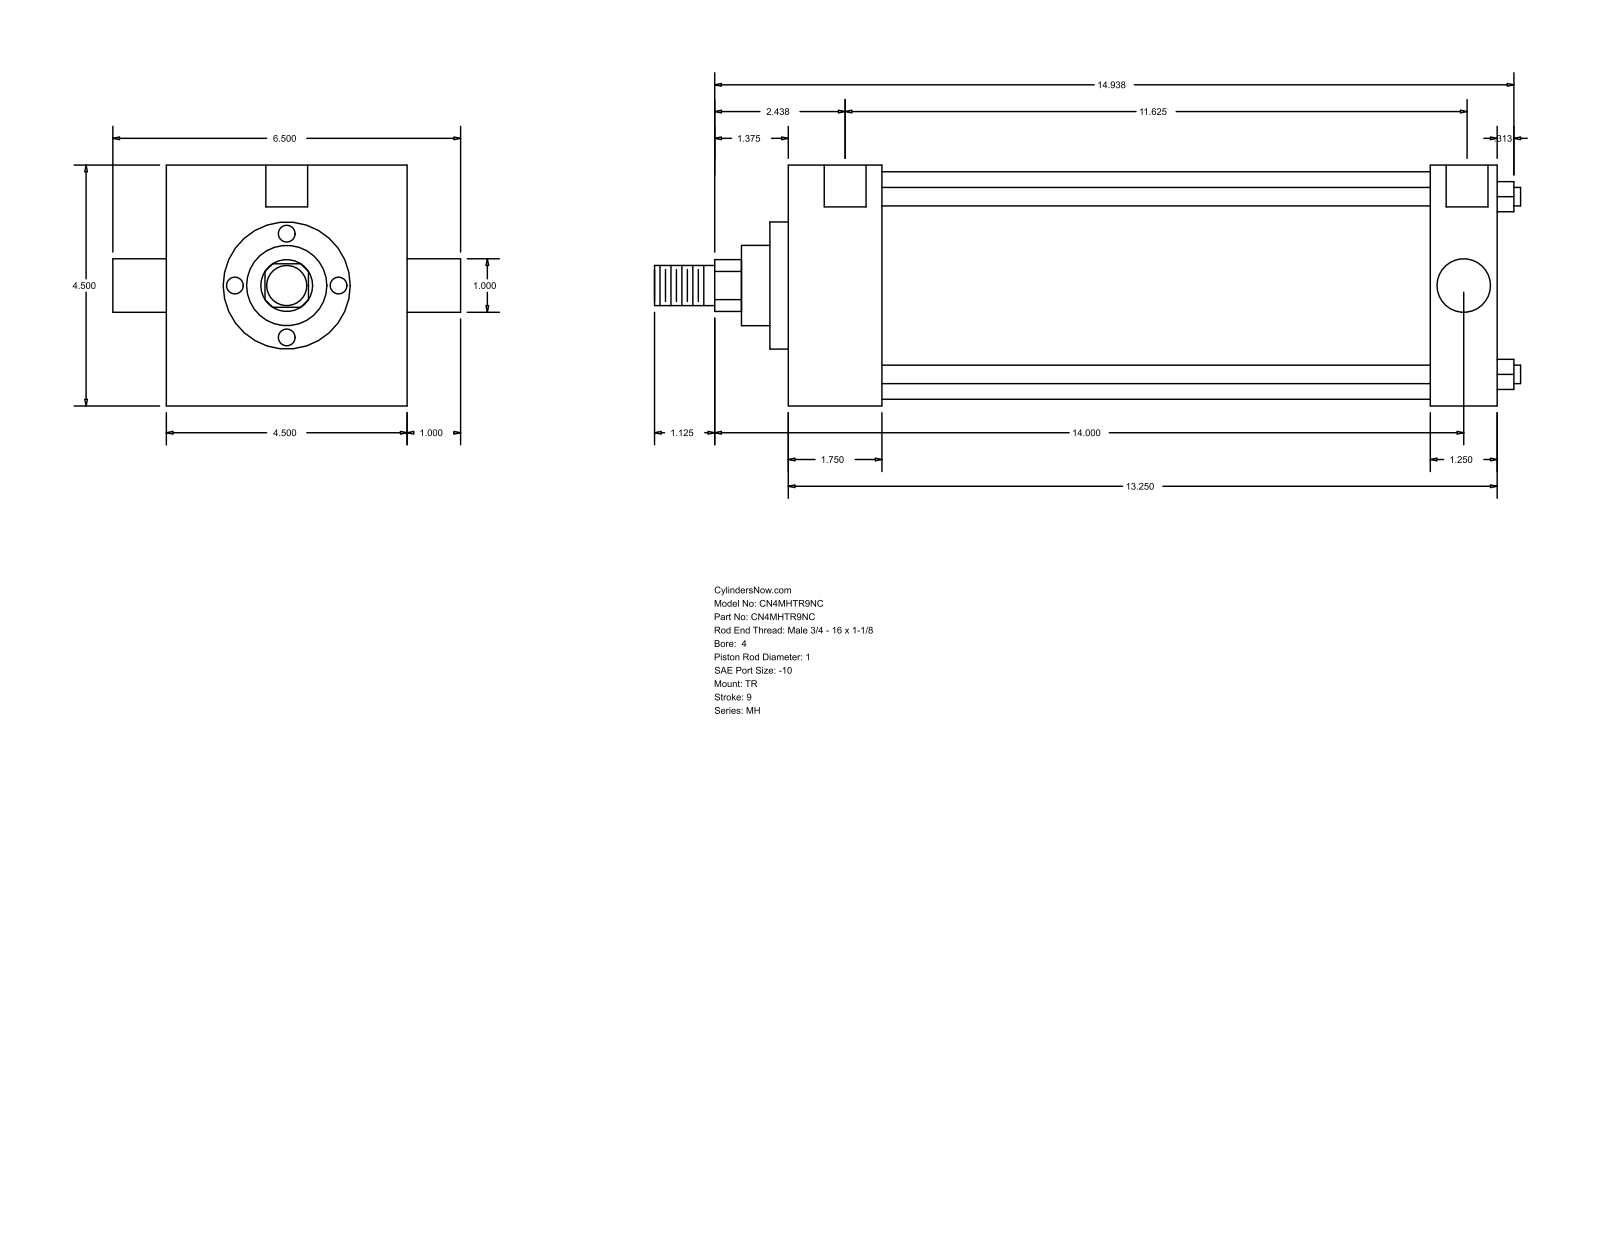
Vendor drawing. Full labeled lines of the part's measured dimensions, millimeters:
Part name (STEP PRODUCT): MH_TR__0400_1
STEP written by: GSSL Pune (CONFIG_CONTROL_DESIGN)
Units: millimetres
Bodies: 0 solids, 86 faces (61 planar, 25 cylindrical, 0 other)
Overall size (bounding box): 411.16 × 165.1 × 114.3
Round holes (diameter × count): ⌀8.73 ×3, ⌀19.84 ×2
Round bosses / shafts (diameter × count): ⌀8.76 ×4, ⌀25.4 ×2, ⌀107.95 ×1, ⌀60.33 ×1, ⌀38.1 ×1, ⌀19.05 ×1
Partial cylindrical surfaces — rounded edges, fillets, slot ends (radius × count): R12.29 ×1
Main face-to-face distances: 114.3, 336.56, 44.46, 292.1, 304.81, 260.35, 31.75, 8.73, 53.19, 313.54
Hole centre spacings: 1.58, 296.86, 295.28, 298.44
